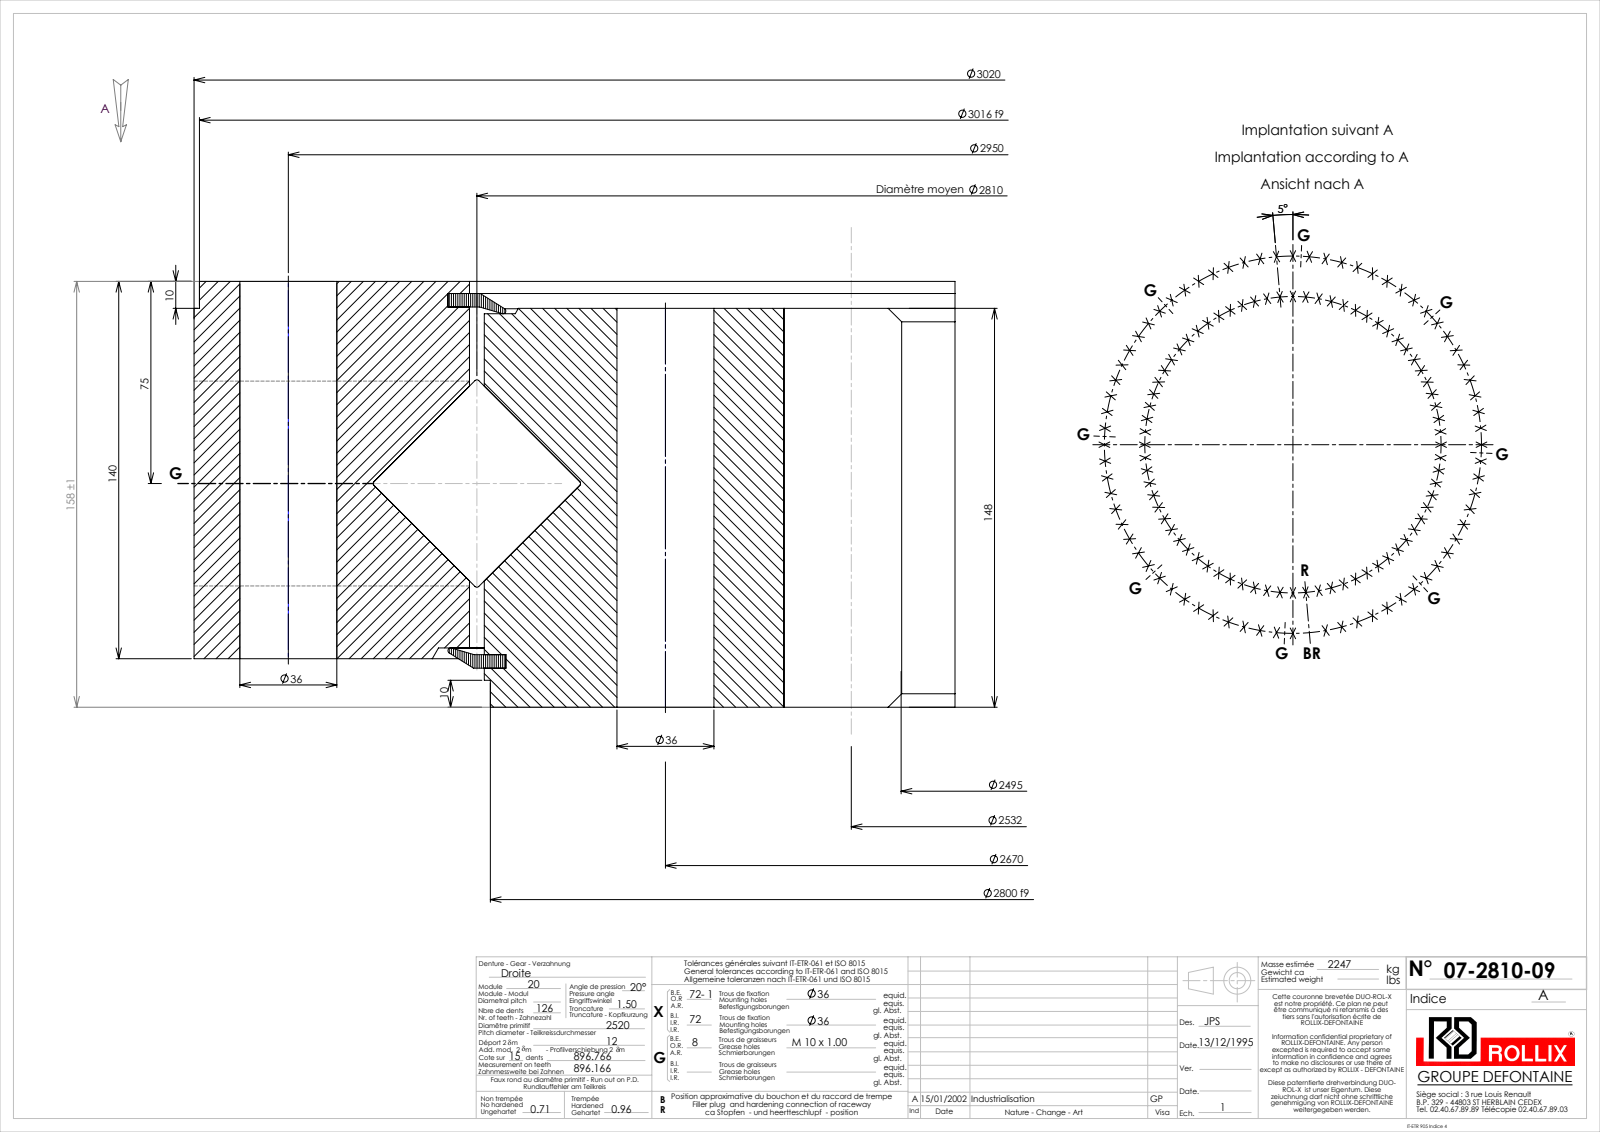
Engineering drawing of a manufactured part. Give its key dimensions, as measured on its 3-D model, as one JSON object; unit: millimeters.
{"part_name": "07-2810-09", "step_written_by": "SolidWorks 2016 (CONFIG_CONTROL_DESIGN)", "units": "millimeters", "bodies": {"solids": 5, "faces": 1148, "planar": 270, "cylindrical": 583, "other": 295}, "overall_size": [3020, 3020, 158], "volume_mm3": 254100000, "surface_area_mm2": 14030000, "round_holes": [[36, 143], [9, 8], [2788.5, 1], [2815.5, 1], [2831.5, 1]], "round_bosses_or_shafts": [[3020, 1], [3016, 1], [2804.5, 1], [2800, 1], [55, 1]], "partial_cylinders_radius": [[1247.5, 1], [1291, 1]], "face_to_face_distances": [148, 10, 158, 18, 130, 140, 5, 134, 7.5, 131.5], "hole_center_spacings": [1335, 463.64, 691.05, 116.47, 232.71, 577.89, 1232.87, 348.5]}
